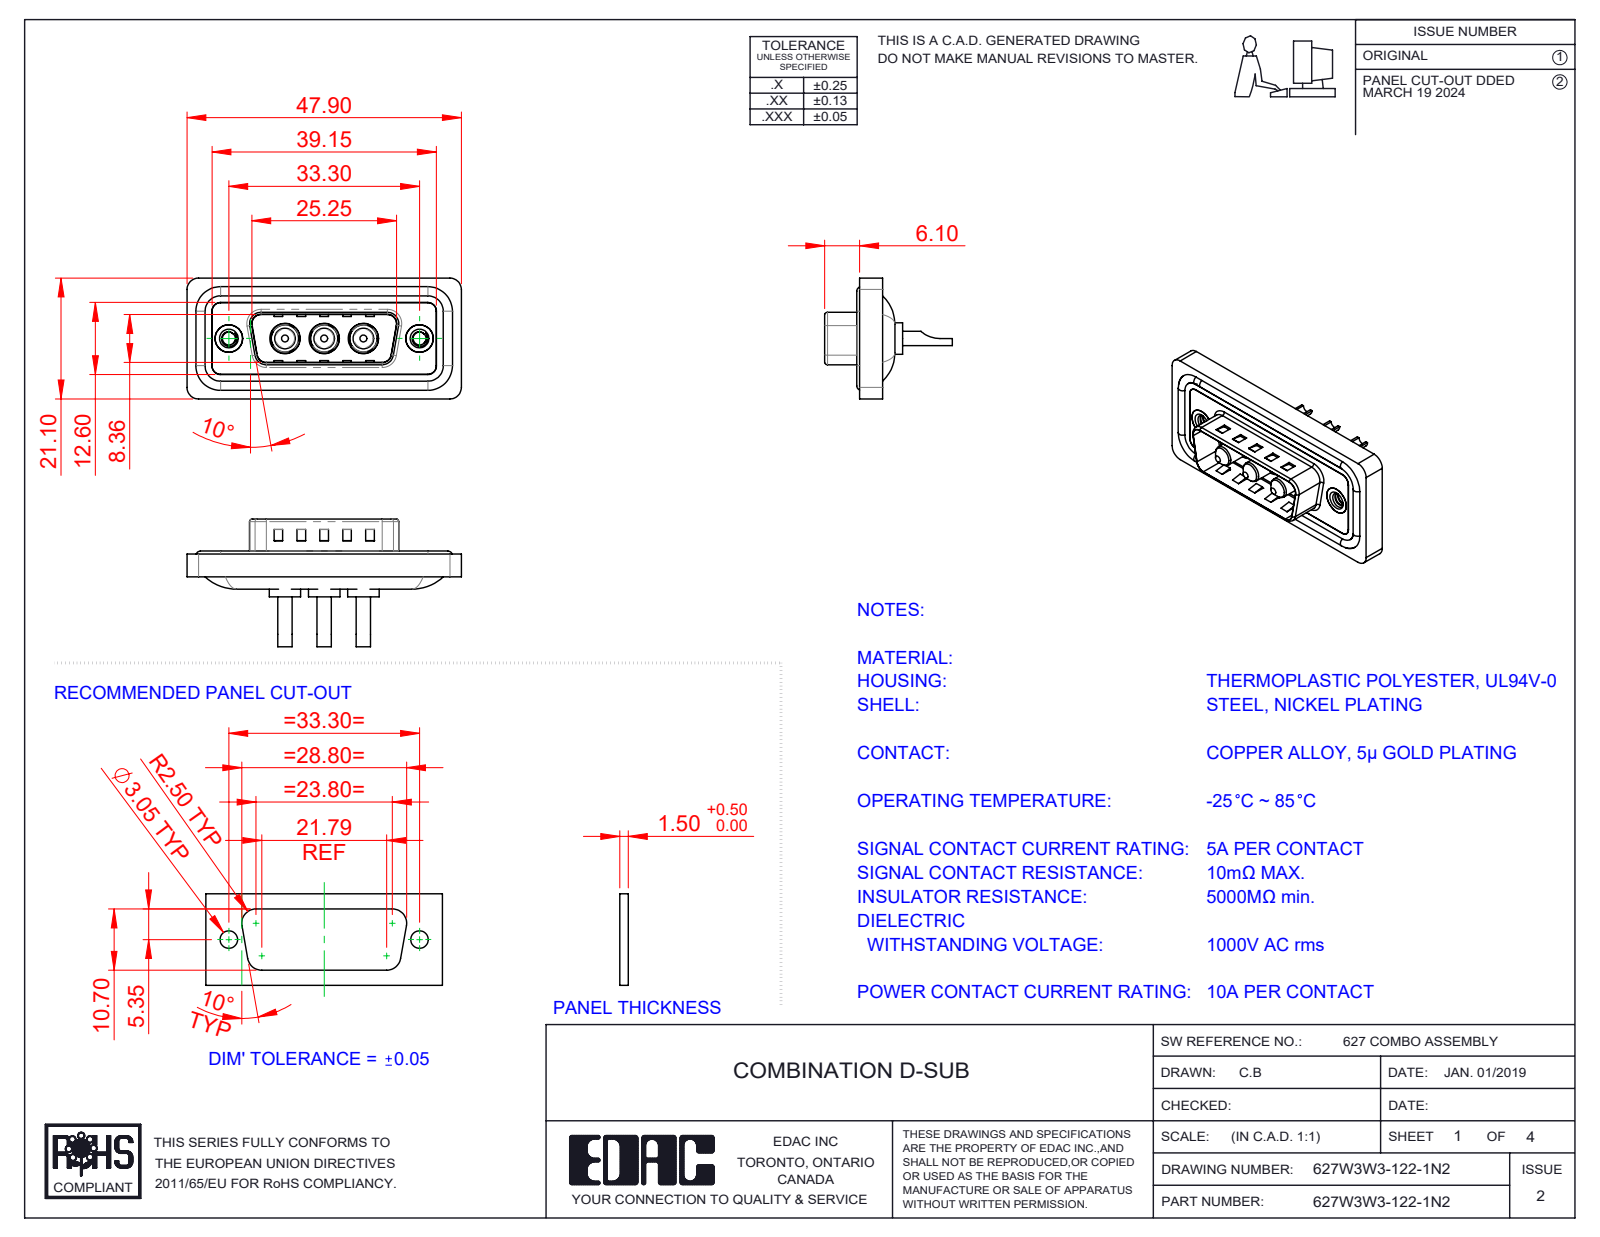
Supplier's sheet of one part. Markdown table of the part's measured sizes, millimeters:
| quantity | value |
| --- | --- |
| part name | 627Combo Threaded Rivet_2; 627Combo Shell Rear_15 Contacts; 627W3W3-122-1N2; 627Combo Shell Front_15 Contacts (+3 more) |
| STEP written by | SolidWorks 2023 (CONFIG_CONTROL_DESIGN) |
| units | millimeters |
| bodies | 13 solids, 579 faces (213 planar, 250 cylindrical, 116 other) |
| overall size | 47.9 × 22.3 × 21.1 |
| volume | 5 577 mm³ |
| surface area | 8 897 mm² |
| round holes (diameter × count) | 1.7 × 3, 4.85 × 3, 5.3 × 3, 2.26 × 2, 4 × 2, 4.8 × 2, 5 × 2 |
| round bosses / shafts (diameter × count) | 1.6 × 4, 5.5 × 3, 5.2 × 3, 4.75 × 3, 3.75 × 3, 3.6 × 3, 2.5 × 3, 4.9 × 2 |
| partial cylindrical surfaces (radius × count) | 1.5 × 26, 2 × 20, 0.5 × 8, 1.6 × 8, 0.25 × 4, 0.6 × 4, 0.65 × 4, 0.9 × 4 |
| main face-to-face distances | 0.4, 1.1, 1.5, 0.5, 1.6, 3.1, 2.9, 4, 0.82, 9.58 |
| hole center spacings | 6.85, 9.8, 16.65, 23.5, 13.7, 33.3 |
